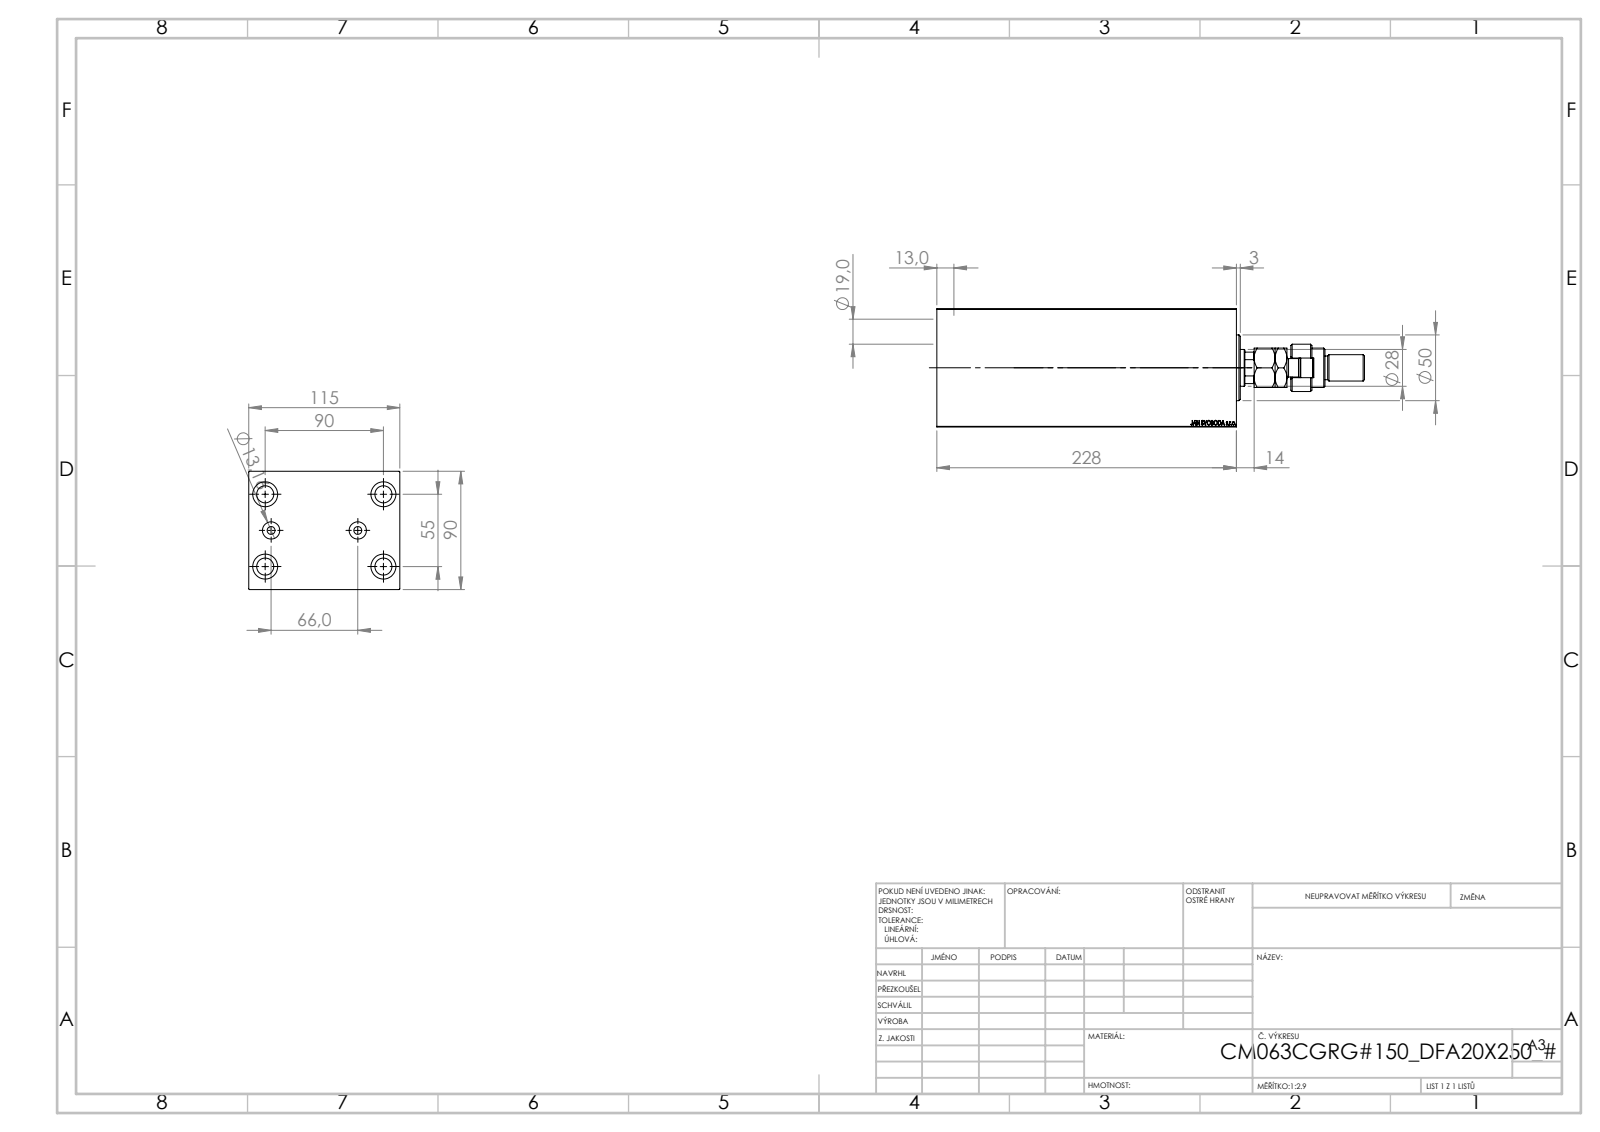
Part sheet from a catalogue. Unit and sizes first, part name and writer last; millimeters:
Units: millimetres
Overall size (bounding box): 325.5 × 115 × 90
Round holes (diameter × count): ⌀13 ×4, ⌀19 ×4, ⌀6 ×2, ⌀13.16 ×2, ⌀18.5 ×1, ⌀28 ×1, ⌀31.5 ×1, ⌀63 ×1, ⌀65 ×1, ⌀72 ×1
Round bosses / shafts (diameter × count): ⌀50 ×1, ⌀36 ×1, ⌀30 ×1, ⌀22 ×1, ⌀20 ×1, ⌀18 ×1, ⌀14 ×1
Partial cylindrical surfaces — rounded edges, fillets, slot ends (radius × count): R7.5 ×1, R12 ×1, R13.5 ×1
Main face-to-face distances: 90, 115, 228, 48.5, 179.5, 218, 10, 5, 169.5, 19.5
Hole centre spacings: 30, 52.74, 82.71, 33, 55, 90, 105.48, 66
Volume: 1 888 000 mm³ · Surface area: 243 229 mm²
Bodies: 5 solids, 946 faces (437 planar, 71 cylindrical, 438 other)
Part name (STEP PRODUCT): V450CM_VC_B; FEMALE_PART_FOR_DFA; V450CM_C_Body; MFA (+1 more)
STEP written by: SolidWorks 2019 (CONFIG_CONTROL_DESIGN)
